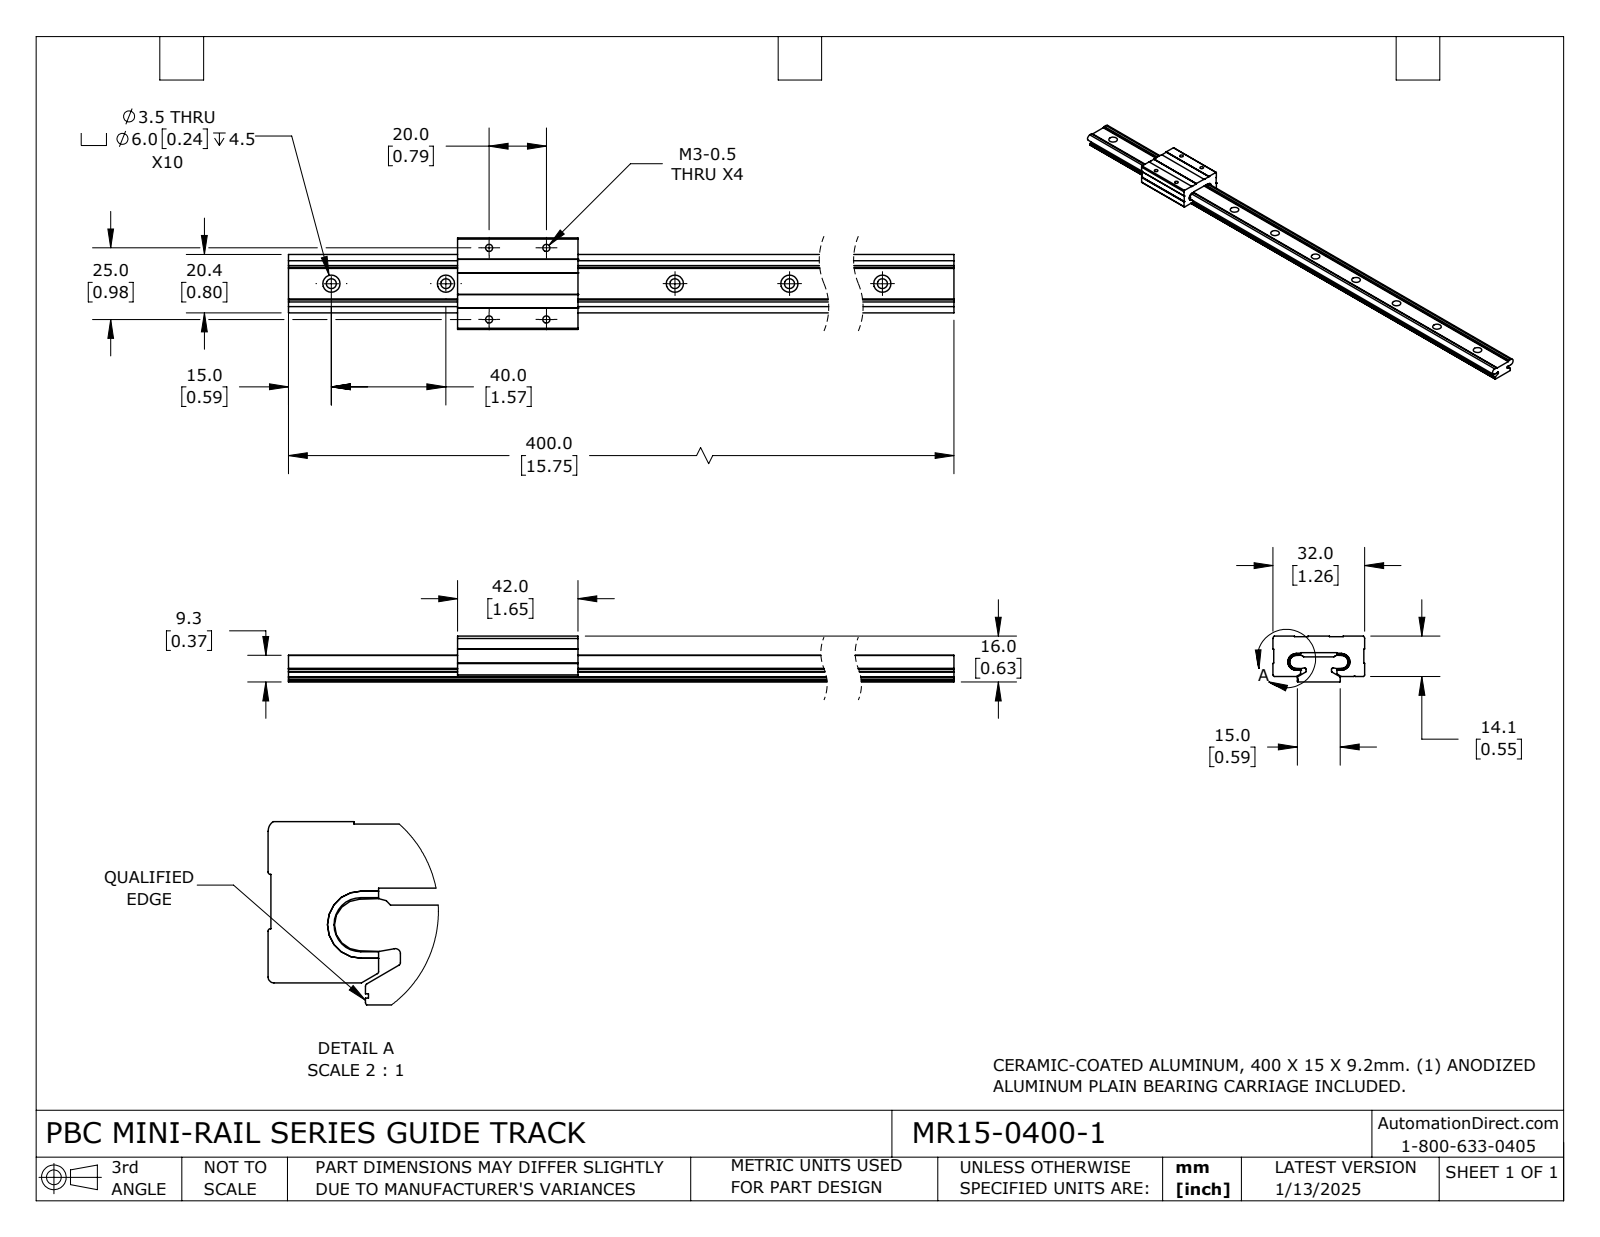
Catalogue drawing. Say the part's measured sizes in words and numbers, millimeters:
The part is named "MR15-0400-1_RAIL; MR15-0400-1_CARRIAGE; MR15-0400-1". Its 3-D file was written by "SolidWorks 2023 (CONFIG_CONTROL_DESIGN)". It is 4 solids with 178 faces: 93 planar, 85 cylindrical and 0 other. Overall it measures 400 by 32 by 16 millimeters. Its volume is 66 840 cubic millimeters and its surface area 35 750 square millimeters. Round holes: 10 of diameter 3.5, 10 of diameter 6, 4 of diameter 2.5. Partial cylindrical surfaces (rounded edges, fillets, slot ends): 12 of radius 0.2, 6 of radius 0.3, 4 of radius 2.3, 2 of radius 0.5, 2 of radius 0.5, 2 of radius 1, 2 of radius 2.3, 2 of radius 2.9. The main face-to-face distances are 8.7, 5, 16, 7.3, 8.5, 23.5, 11.6, 20.4, 3, 11.9. The hole center spacings are 40, 80, 120, 160, 200, 240, 280, 13.4.
